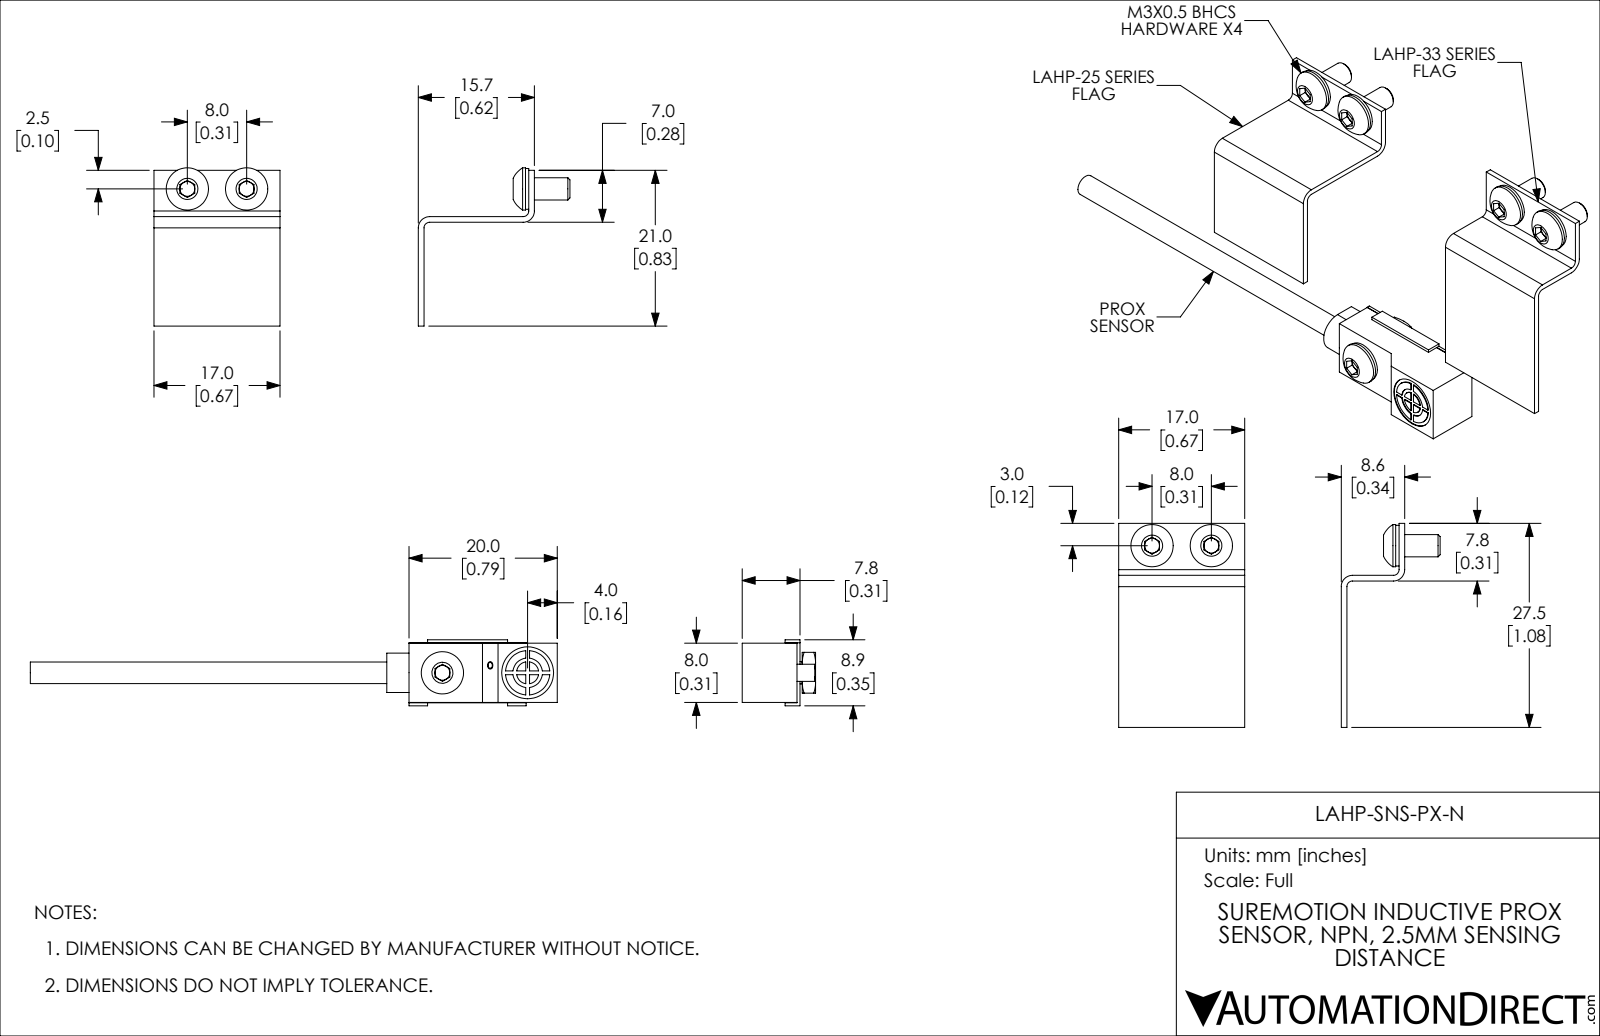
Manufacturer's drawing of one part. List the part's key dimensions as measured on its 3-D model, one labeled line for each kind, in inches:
Part name (STEP PRODUCT): LAHP-SNS-PX-N_25-FLAG; LAHP-SNS-PX-N; LAHP-SNS-PX-N_PROX; LAHP-SNS-PX-N_33-FLAG
STEP written by: SolidWorks 2019 (CONFIG_CONTROL_DESIGN)
Units: inches
Bodies: 15 solids, 328 faces (179 planar, 90 cylindrical, 59 other)
Overall size (bounding box): 3.705 × 1.803 × 0.813
Volume: 0.166 in³ · Surface area: 7.767 in²
Round holes (diameter × count): ⌀0.126 ×5, ⌀0.134 ×4, ⌀0.039 ×1, ⌀0.118 ×1, ⌀0.122 ×1, ⌀0.157 ×1, ⌀0.276 ×1
Round bosses / shafts (diameter × count): ⌀0.224 ×5, ⌀0.217 ×5, ⌀0.118 ×4, ⌀0.236 ×1, ⌀0.114 ×1, ⌀0.031 ×1
Partial cylindrical surfaces — rounded edges, fillets, slot ends (radius × count): R0.03 ×4, R0.06 ×4, R0.059 ×1, R0.104 ×1
Main face-to-face distances: 0.03, 0.28, 0.307, 0.587, 0.406, 0.435, 0.309, 0.128, 0.277, 0.685
Hole centre spacings: 0.315, 1.457, 0.453, 1.142, 1.52, 1.576, 1.601, 1.62
